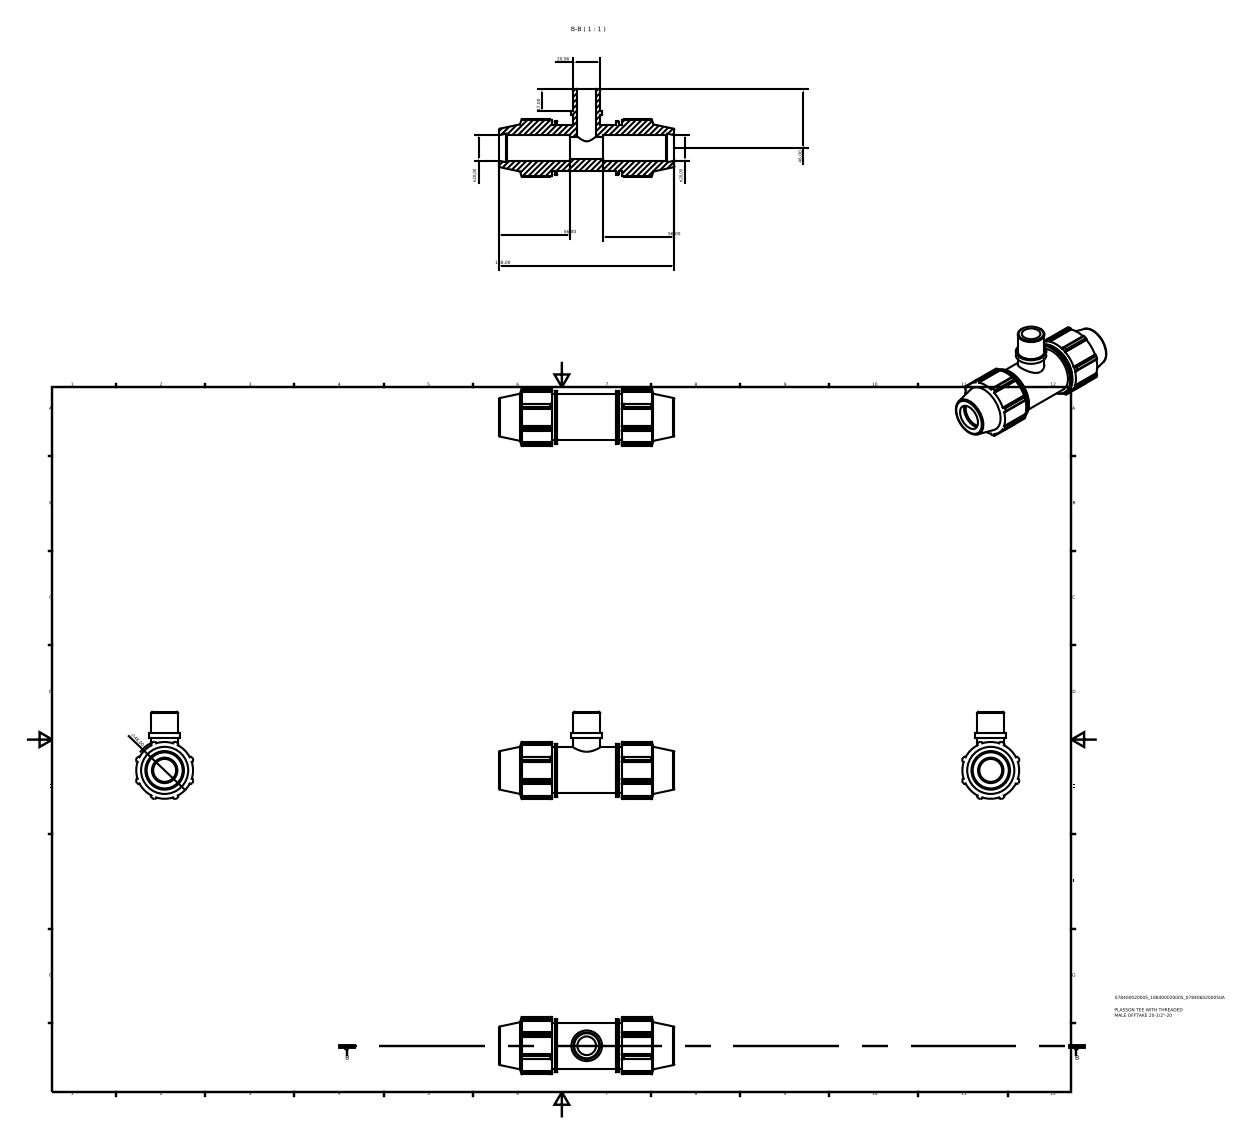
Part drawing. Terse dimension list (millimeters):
name: 078400020005_188400020005
written by: Autodesk Inventor 2015 (AUTOMOTIVE_DESIGN)
unit: mm
bodies: 1 solid, 154 faces (79 planar, 44 cylindrical, 31 other)
size: 138 × 68.58 × 45.16
volume: 127 991 mm³; area: 34 121 mm²
holes: 1× ⌀14.67, 1× ⌀18, 1× ⌀20
bosses: 1× ⌀41.76, 1× ⌀36, 1× ⌀24.1, 1× ⌀20.95
rounds: 1× R22.32, 1× R24
face distances: 2.3, 50.6, 46, 41.4, 96.6, 43.7, 94.3, 52.9, 92, 4.6
